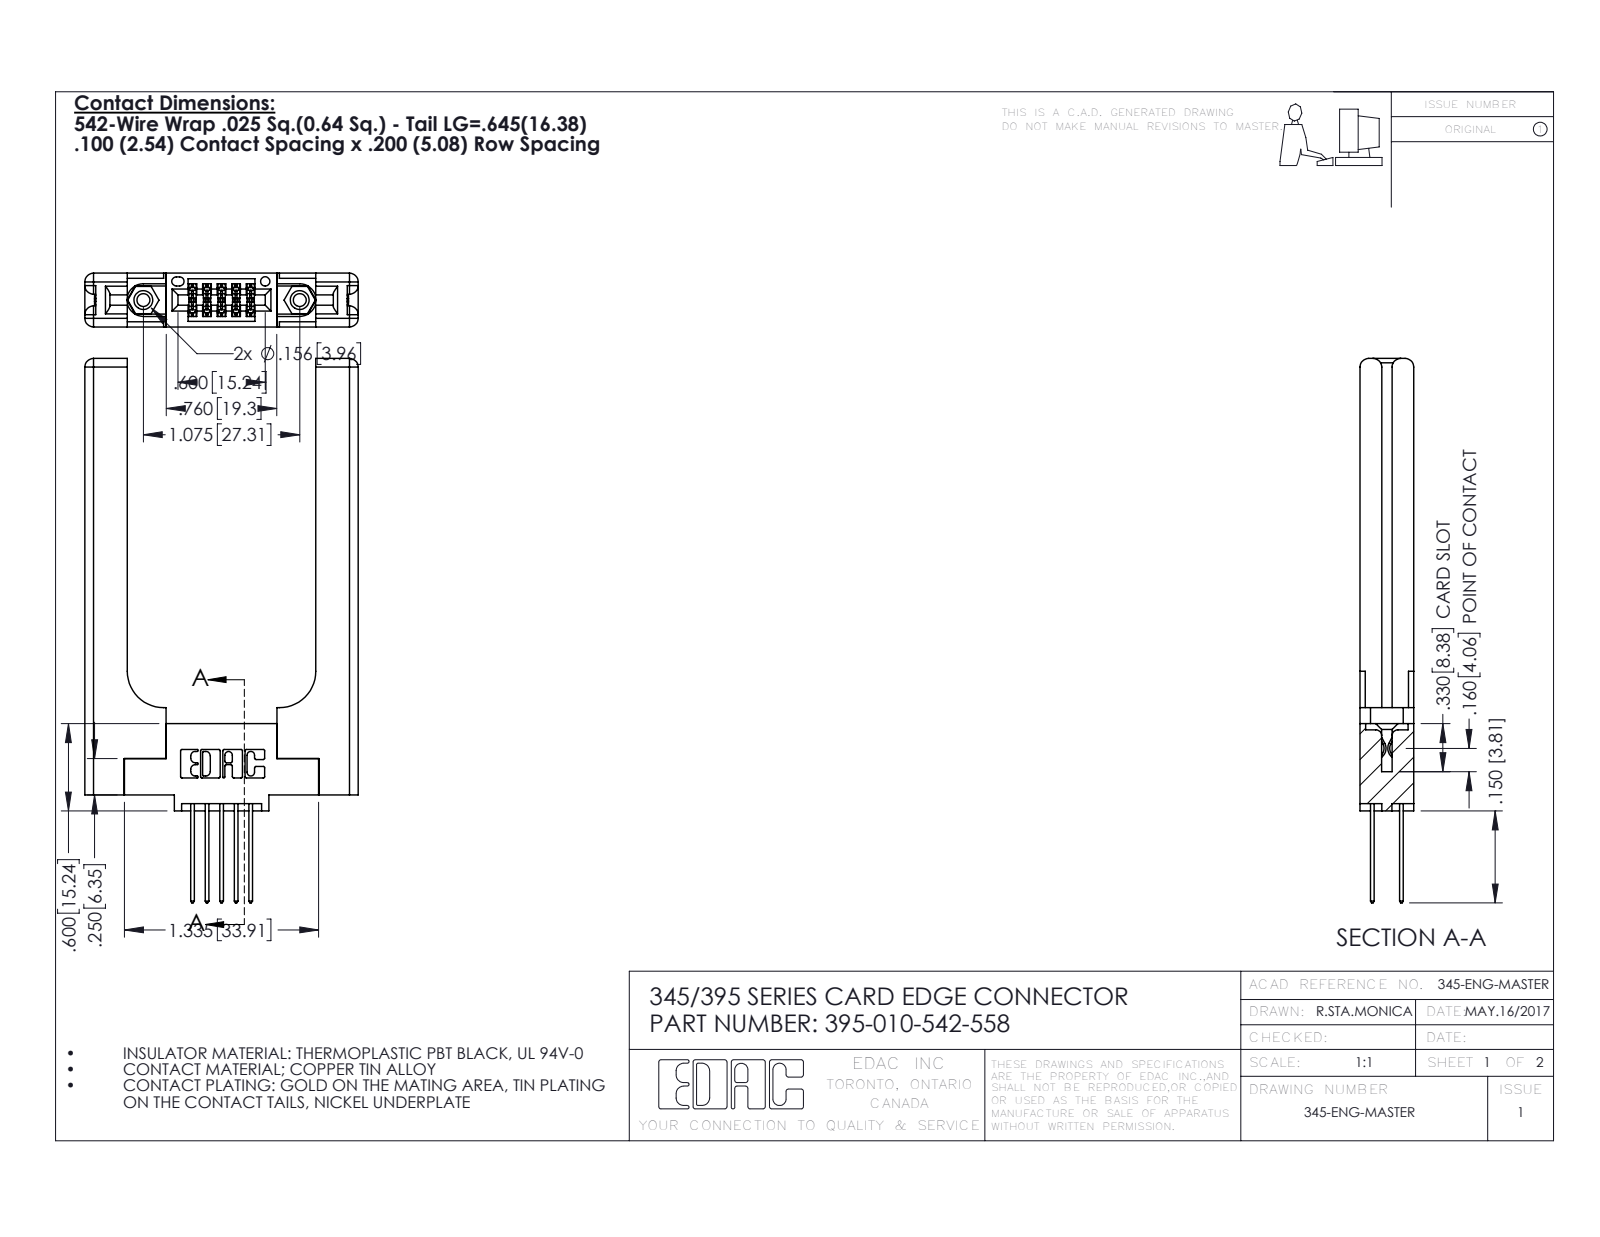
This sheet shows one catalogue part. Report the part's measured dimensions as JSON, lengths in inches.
{"part_name": "345-292-001_345-293-142; 345 Part_0.110 Offset - 0.156 Dia-TH; 395-010-542-558; 345-250-001_345-250-001-102 (+1 more)", "step_written_by": "SolidWorks 2016 (CONFIG_CONTROL_DESIGN)", "units": "inches", "bodies": {"solids": 15, "faces": 886, "planar": 562, "cylindrical": 264, "other": 60}, "overall_size": [3.742, 1.879, 0.37], "volume_in3": 0.778, "surface_area_in2": 16.99, "round_holes": [[0.089, 2], [0.125, 2], [0.156, 2], [0.064, 1]], "round_bosses_or_shafts": [[0.155, 2]], "partial_cylinders_radius": [[0.01, 22], [0.06, 16], [0.006, 15], [0.01, 10], [0.007, 6], [0.031, 6], [0.026, 3], [0.014, 2]], "face_to_face_distances": [0.37, 0.15, 0.22, 0.072, 0.148, 0.077, 0.298, 1.296, 0.071, 0.292], "hole_center_spacings": [0.27, 0.847, 1.075]}
